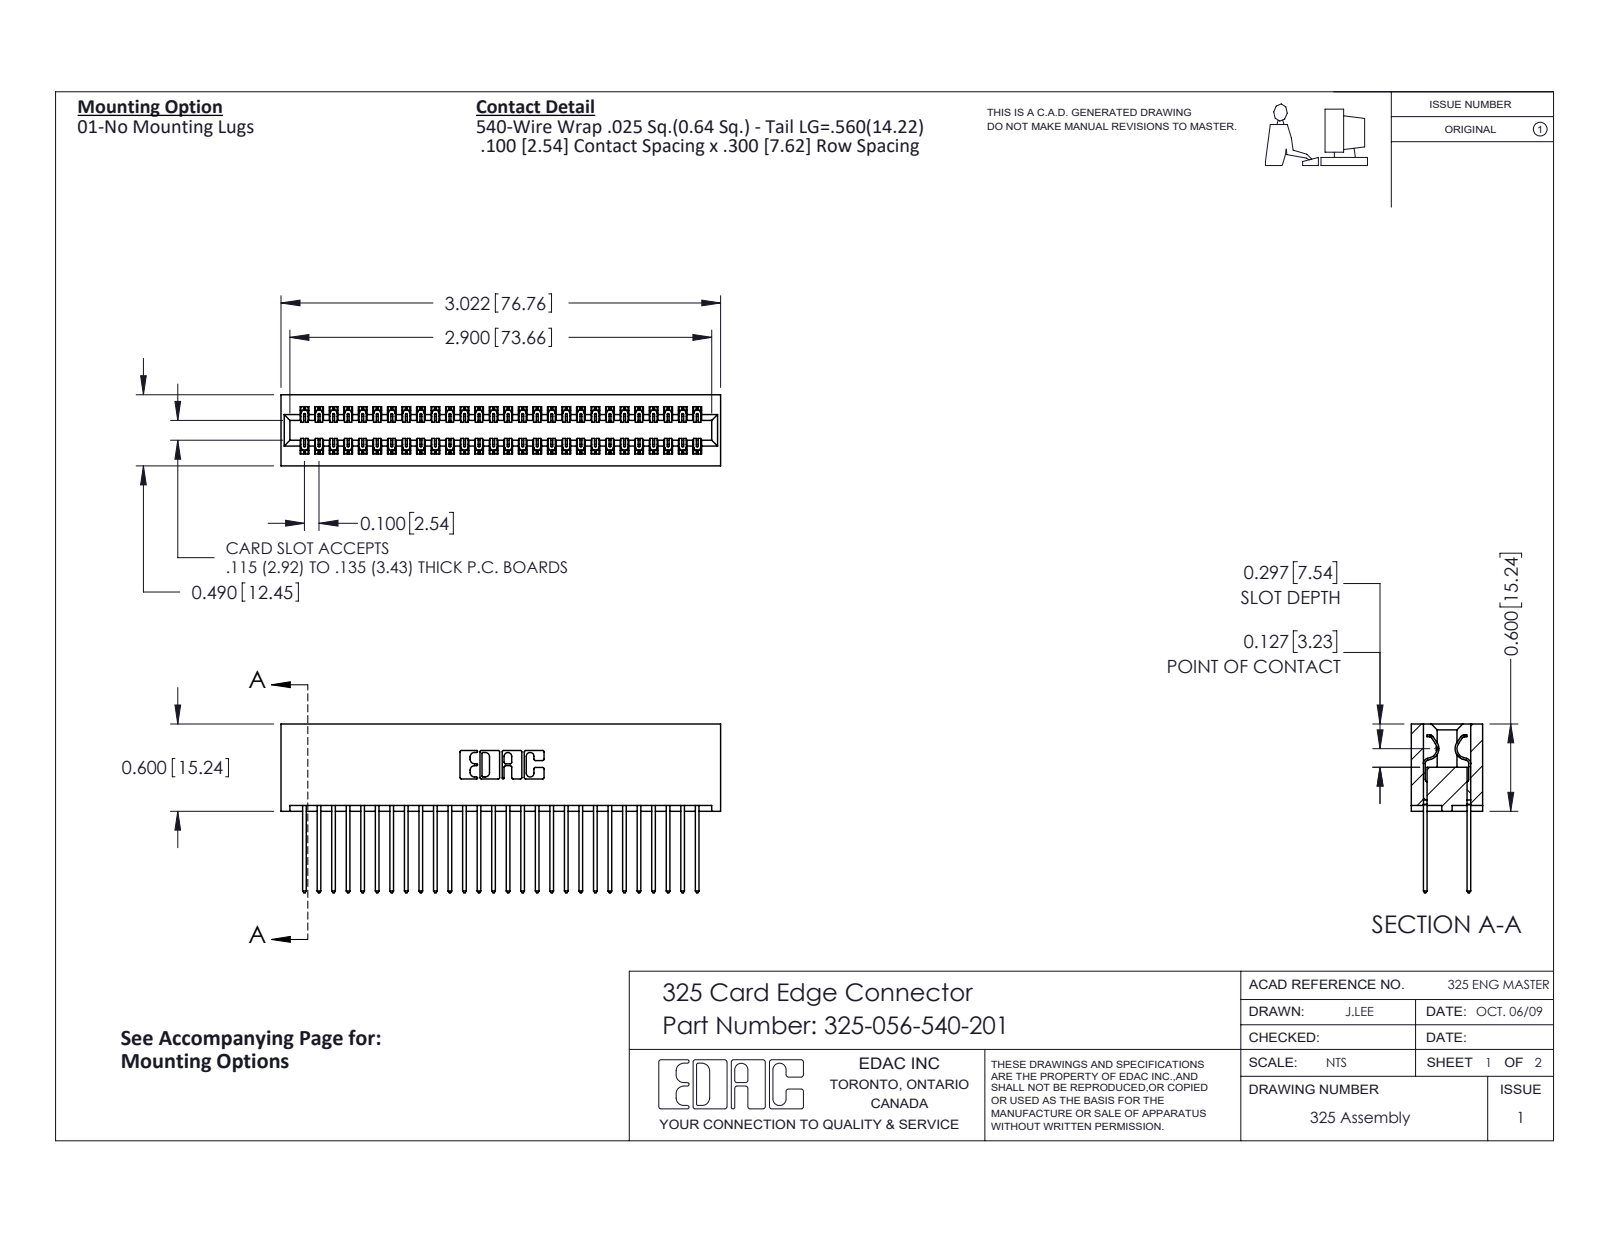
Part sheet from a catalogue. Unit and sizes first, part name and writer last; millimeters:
Units: millimetres
Overall size (bounding box): 76.8 × 29.5 × 12.4
Partial cylindrical surfaces — rounded edges, fillets, slot ends (radius × count): R0.2 ×84, R0.3 ×56, R0.3 ×22, R0.2 ×6, R0.8 ×6, R0.7 ×3, R0.4 ×2, R0.6 ×2
Main face-to-face distances: 2.1, 10.3, 7.6, 2.7, 9.7, 0.6, 8.3, 12.4, 7, 14.2
Volume: 10 600 mm³ · Surface area: 14 170 mm²
Bodies: 57 solids, 3018 faces (2082 planar, 936 cylindrical, 0 other)
Part name (STEP PRODUCT): 325-056-540-201; 325-292-001_325-293-140; 325 Part_Lugless
STEP written by: SolidWorks 2016 (CONFIG_CONTROL_DESIGN)
